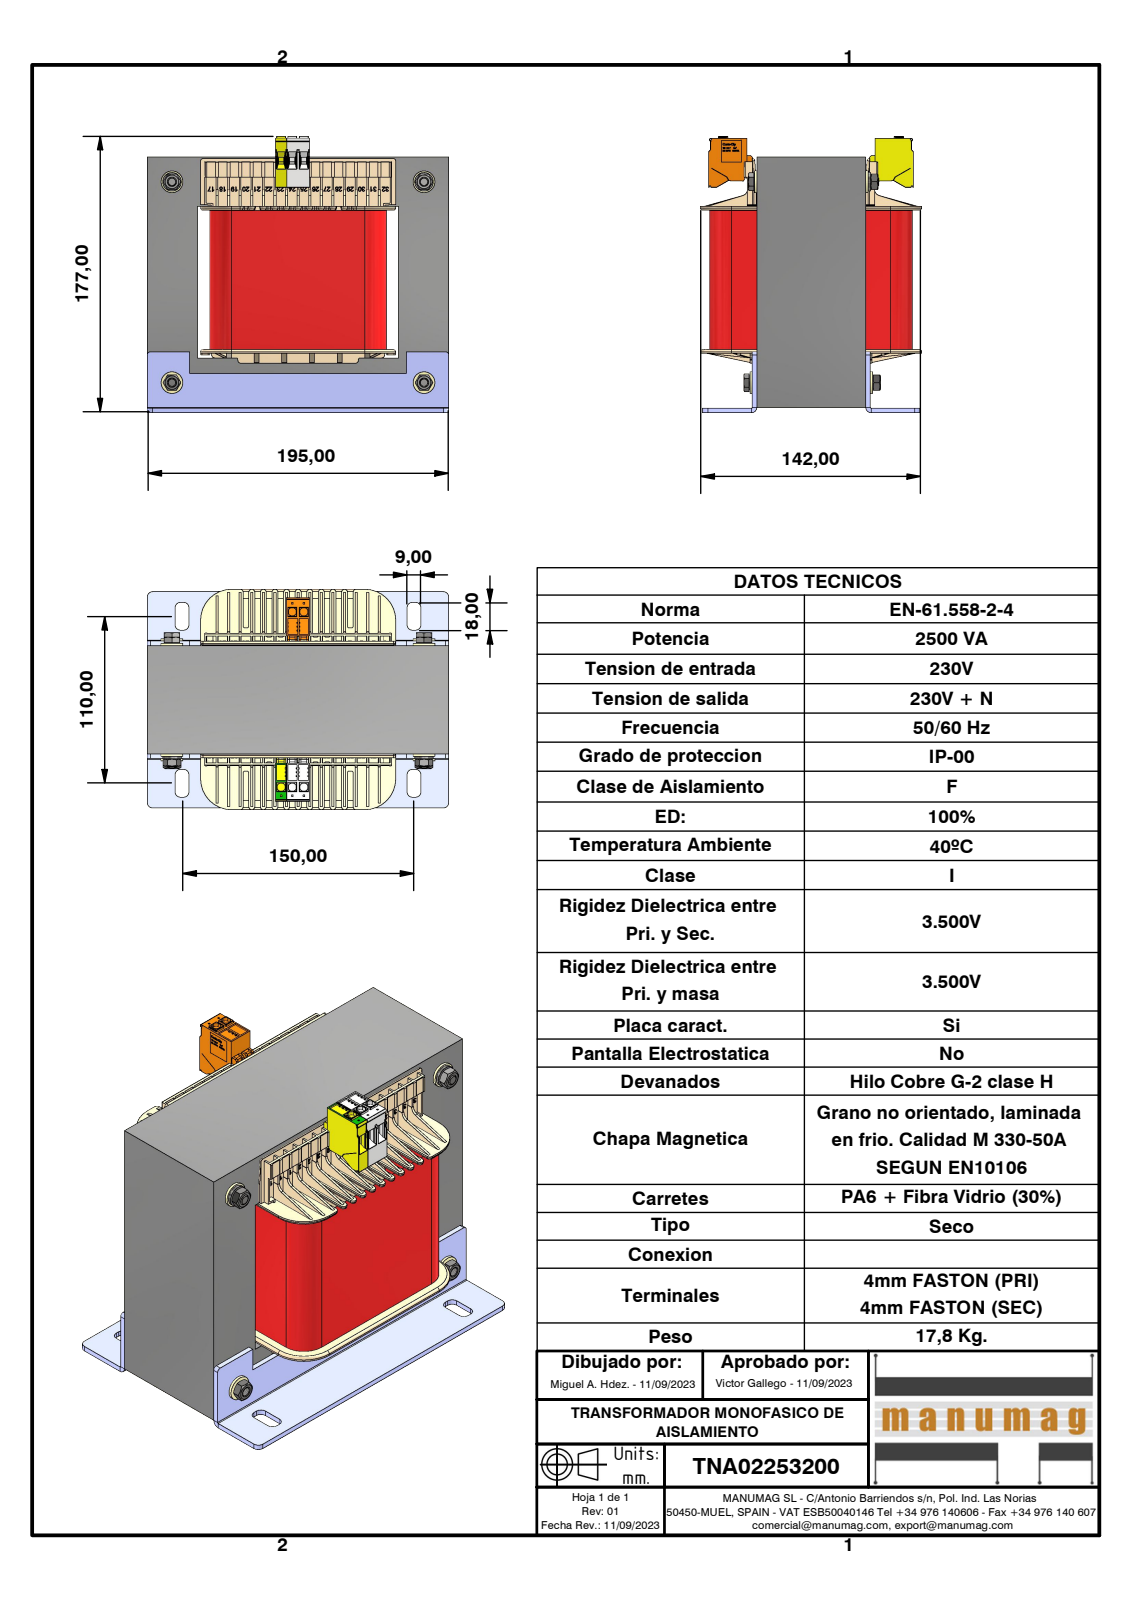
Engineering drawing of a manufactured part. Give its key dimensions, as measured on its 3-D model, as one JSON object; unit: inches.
{"part_name": "TNA02253200; EI195 x 162 - 70 (Rc65); EI192_70_AK_25379_8_Wz837 Con bobinado; 195 (+7 more)", "step_written_by": "Autodesk Inventor 2023 (AUTOMOTIVE_DESIGN)", "units": "inches", "bodies": {"solids": 25, "faces": 7304, "planar": 5161, "cylindrical": 810, "other": 1333}, "overall_size": [7.677, 7.047, 5.614], "volume_in3": 122.2, "surface_area_in2": 631.3, "round_holes": [[0.194, 4], [0.236, 4], [0.433, 4], [0.252, 2], [0.39, 2]], "round_bosses_or_shafts": [[0.551, 4], [0.343, 4], [0.299, 4], [0.215, 4], [0.472, 2]], "partial_cylinders_radius": [[0.006, 188], [0.008, 74], [0.039, 52], [0.059, 44], [0.02, 30], [0.077, 22], [0.138, 22], [0.012, 12]], "face_to_face_distances": [5.118, 0.118, 1.28, 2.756, 6.398, 2.874, 2.559, 1.26, 3.646, 0.094], "hole_center_spacings": [5.118, 6.417, 8.208]}
